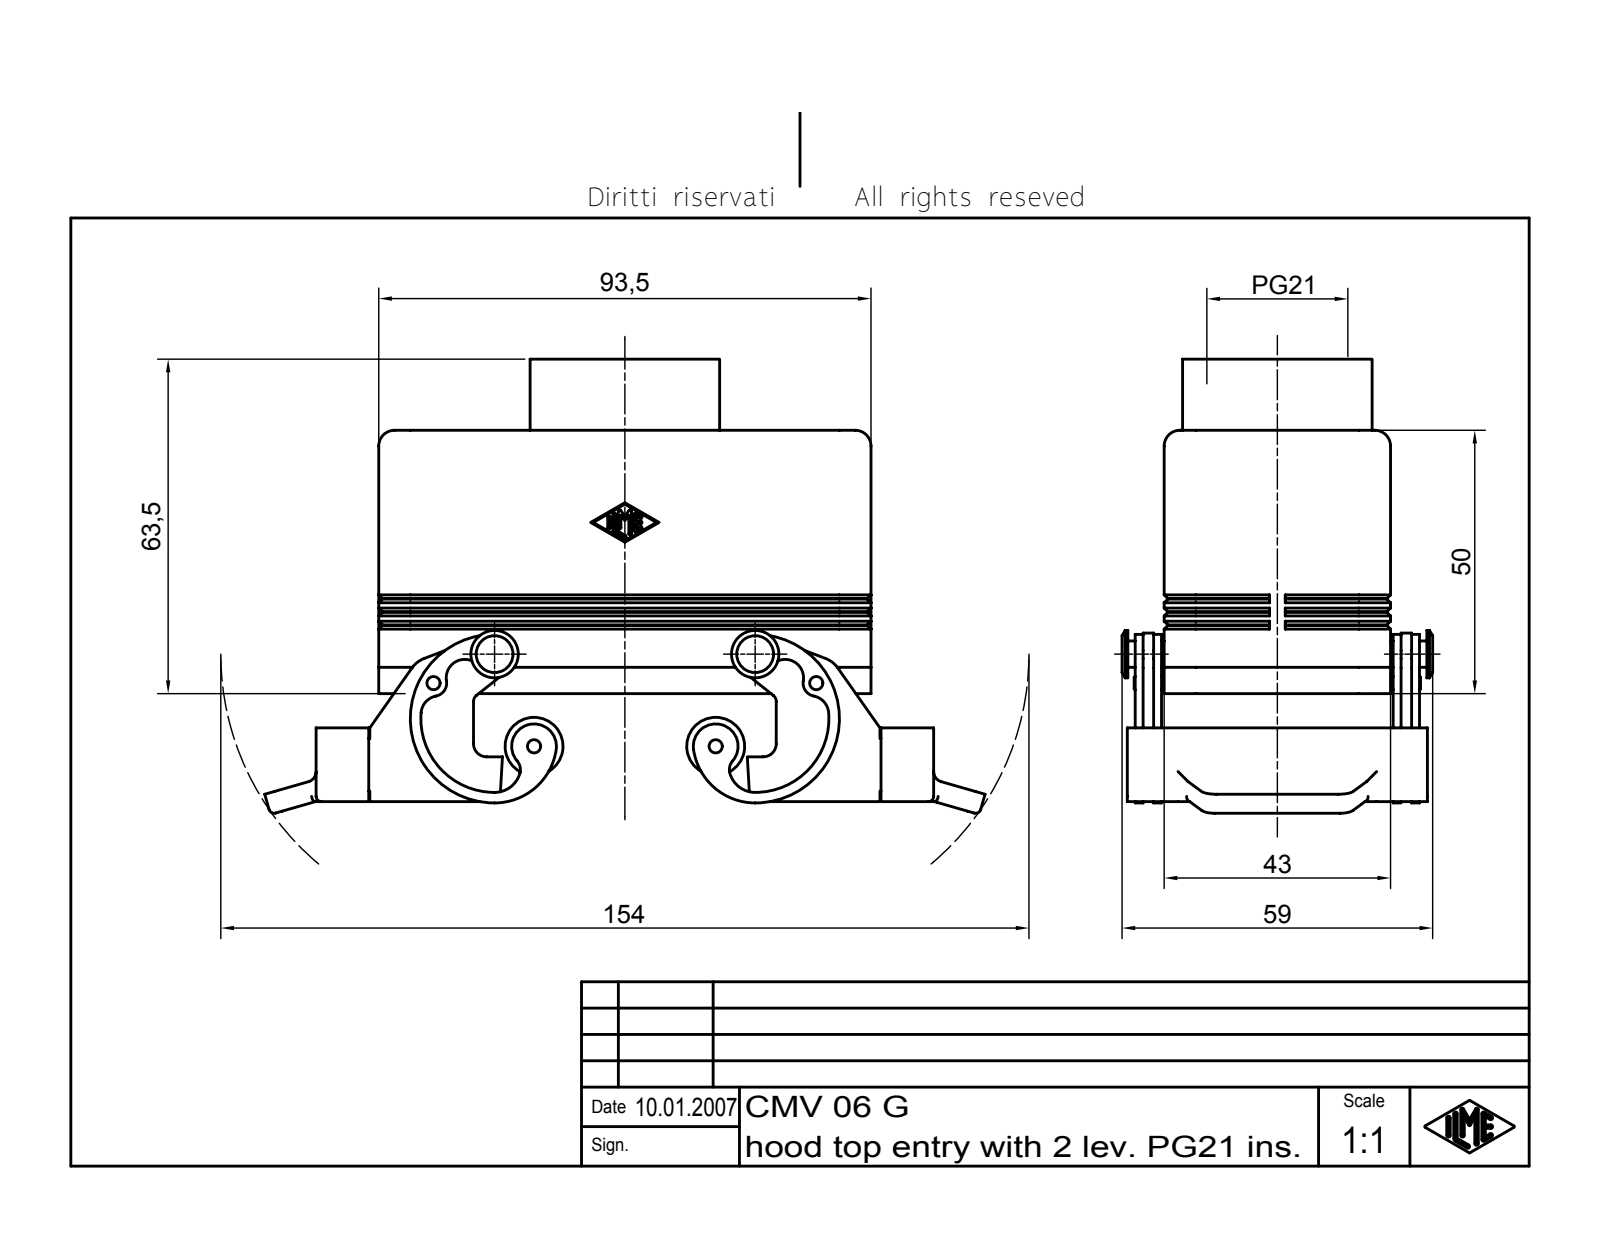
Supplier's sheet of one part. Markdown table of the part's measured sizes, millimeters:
| quantity | value |
| --- | --- |
| part name | CHV Tüllengehäuse 2 Bügel für einen Einsatz |
| STEP written by | Autodesk Inventor 7 (AUTOMOTIVE_DESIGN) |
| units | millimeters |
| bodies | 1 solid, 771 faces (228 planar, 207 cylindrical, 336 other) |
| overall size | 136.82 × 86.21 × 59 |
| volume | 83 088 mm³ |
| surface area | 51 762 mm² |
| round holes (diameter × count) | 2.5 × 2, 21.62 × 1, 26.78 × 1 |
| round bosses / shafts (diameter × count) | 11 × 2, 9 × 2, 5 × 2, 2 × 2, 36 × 1 |
| partial cylindrical surfaces (radius × count) | 0.25 × 14, 3 × 12, 2 × 10, 1 × 8, 2.5 × 6, 3 × 4, 3.5 × 4, 5 × 4 |
| main face-to-face distances | 3, 40, 37, 43, 8.5, 47, 11.5, 2, 90.5, 5 |
| hole center spacings | 72.7 |
